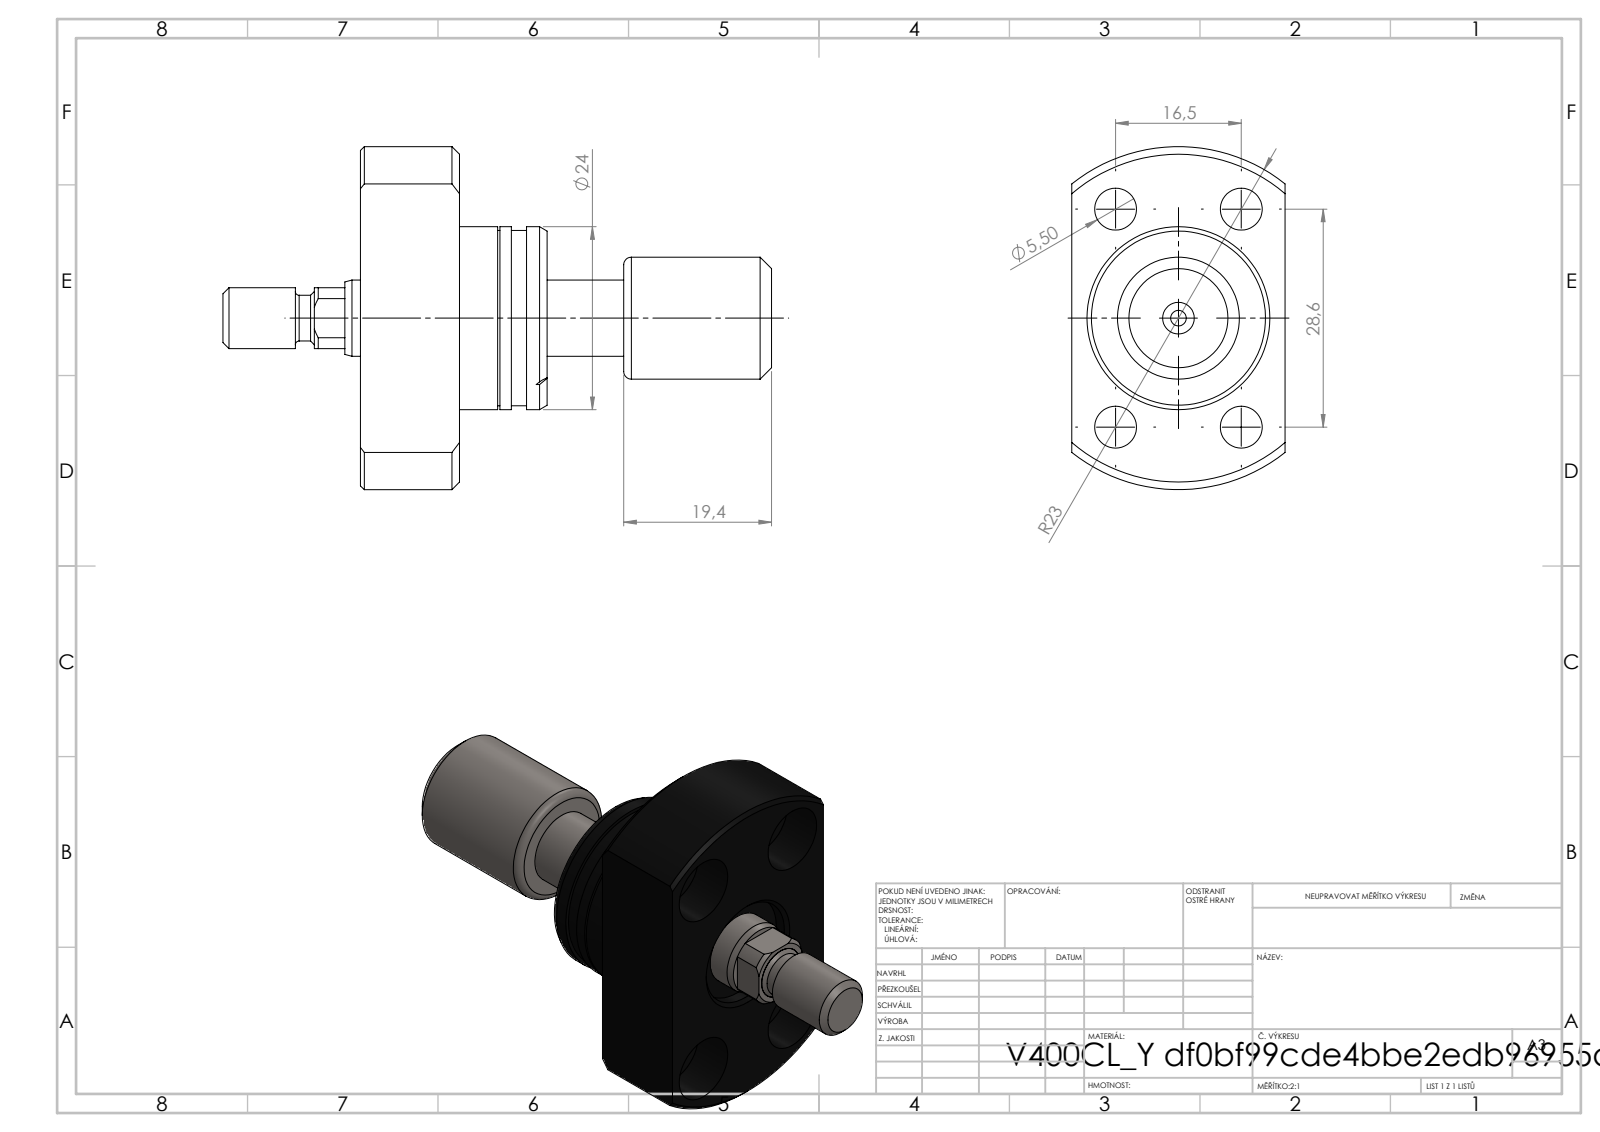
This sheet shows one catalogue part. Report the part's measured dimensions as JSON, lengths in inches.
{"part_name": "V400CL_PC_Y; V400CL_VC_X; V450CM_MALE_METRIC", "step_written_by": "SolidWorks 2019 (CONFIG_CONTROL_DESIGN)", "units": "inches", "bodies": {"solids": 3, "faces": 116, "planar": 29, "cylindrical": 51, "other": 36}, "overall_size": [2.835, 1.772, 1.102], "volume_in3": 1.403, "surface_area_in2": 15.31, "round_holes": [[0.217, 4], [0.354, 4], [0.081, 1], [0.197, 1], [0.236, 1], [0.394, 1], [0.571, 1]], "round_bosses_or_shafts": [[0.945, 1], [0.906, 1], [0.63, 1], [0.315, 1]], "partial_cylinders_radius": [[0.187, 1], [0.886, 1]], "face_to_face_distances": [0.512, 1.102, 0.453, 0.965, 0.748, 0.295, 0.217, 0.079, 0.138, 1.159], "hole_center_spacings": [0.65, 0.65, 1.126, 1.3]}
